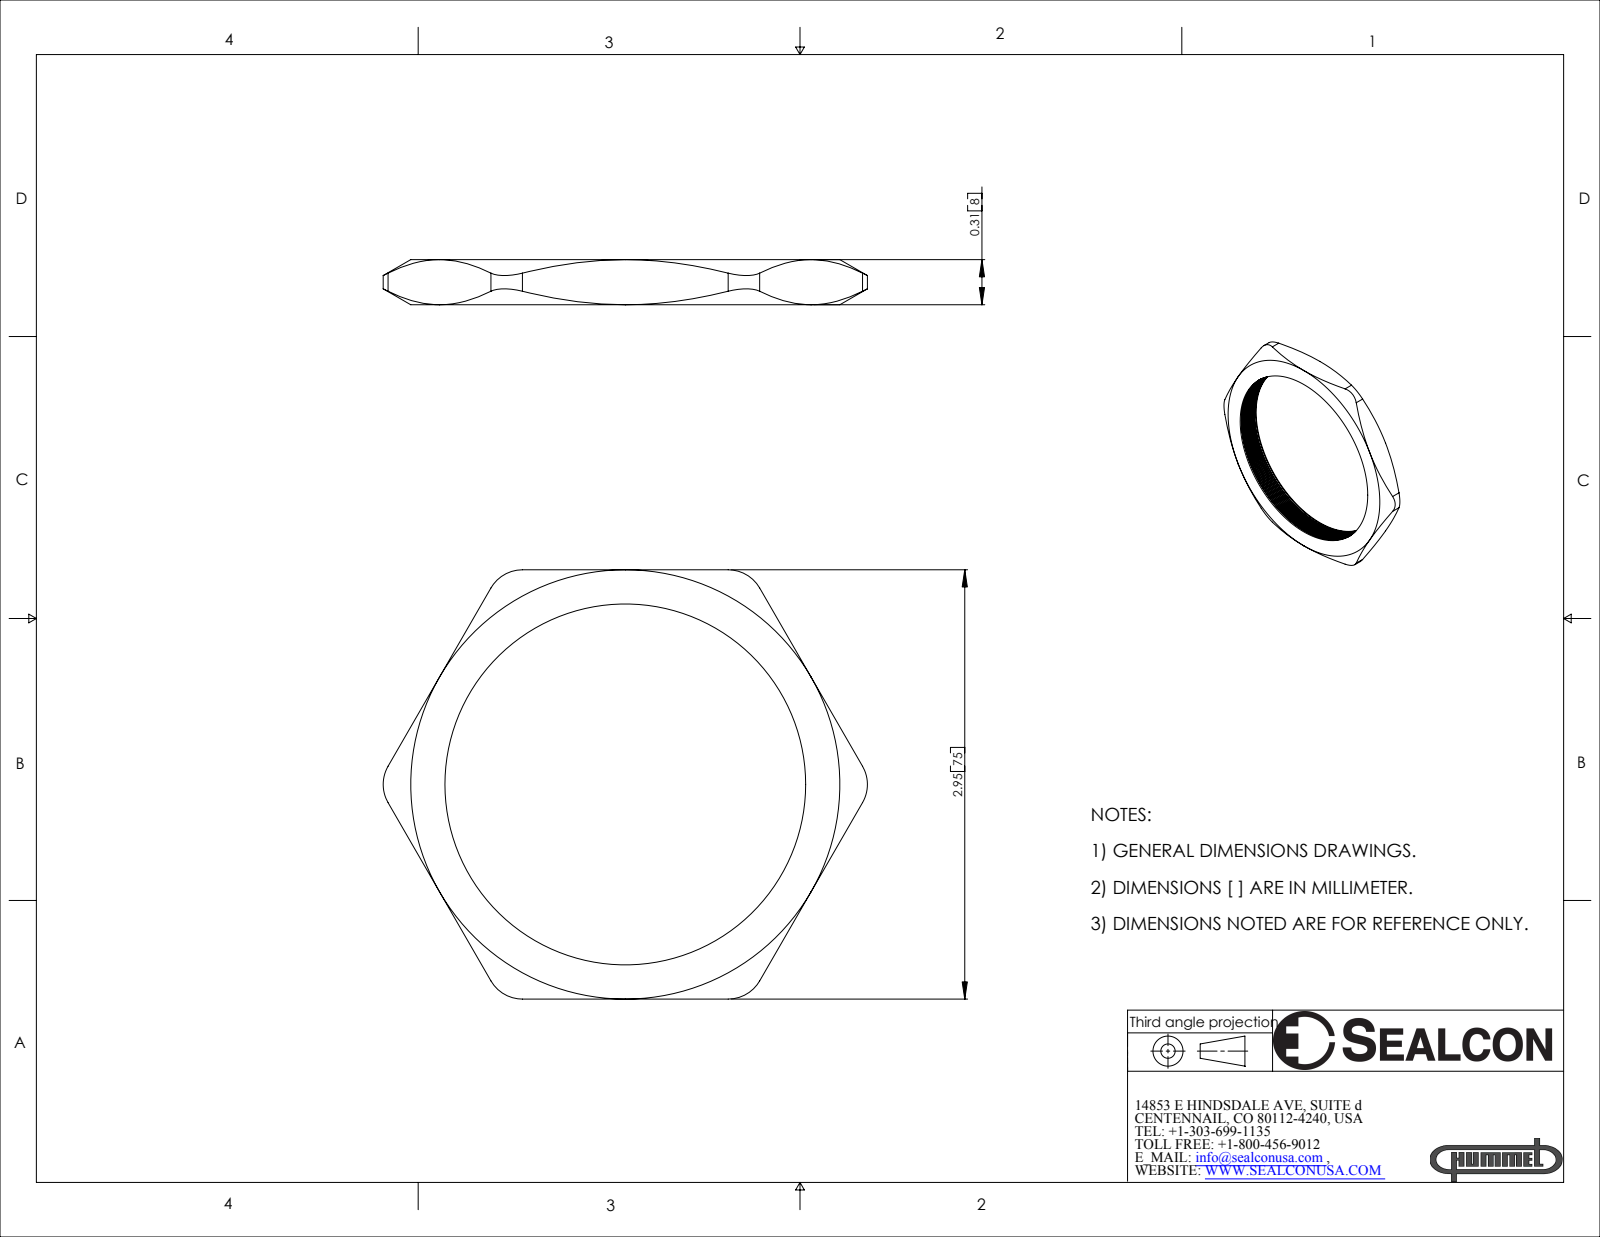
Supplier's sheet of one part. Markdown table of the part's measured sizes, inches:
| quantity | value |
| --- | --- |
| part name | NM-63 |
| STEP written by | SolidWorks 2007 (CONFIG_CONTROL_DESIGN) |
| units | inches |
| bodies | 1 solid, 101 faces (8 planar, 31 cylindrical, 62 other) |
| overall size | 3.329 × 2.95 × 0.31 |
| volume | 0.76 in³ |
| surface area | 12.45 in² |
| round holes (diameter × count) | 2.48 × 1 |
| partial cylindrical surfaces (radius × count) | 0.25 × 6 |
| main face-to-face distances | 0.31, 2.95 |
